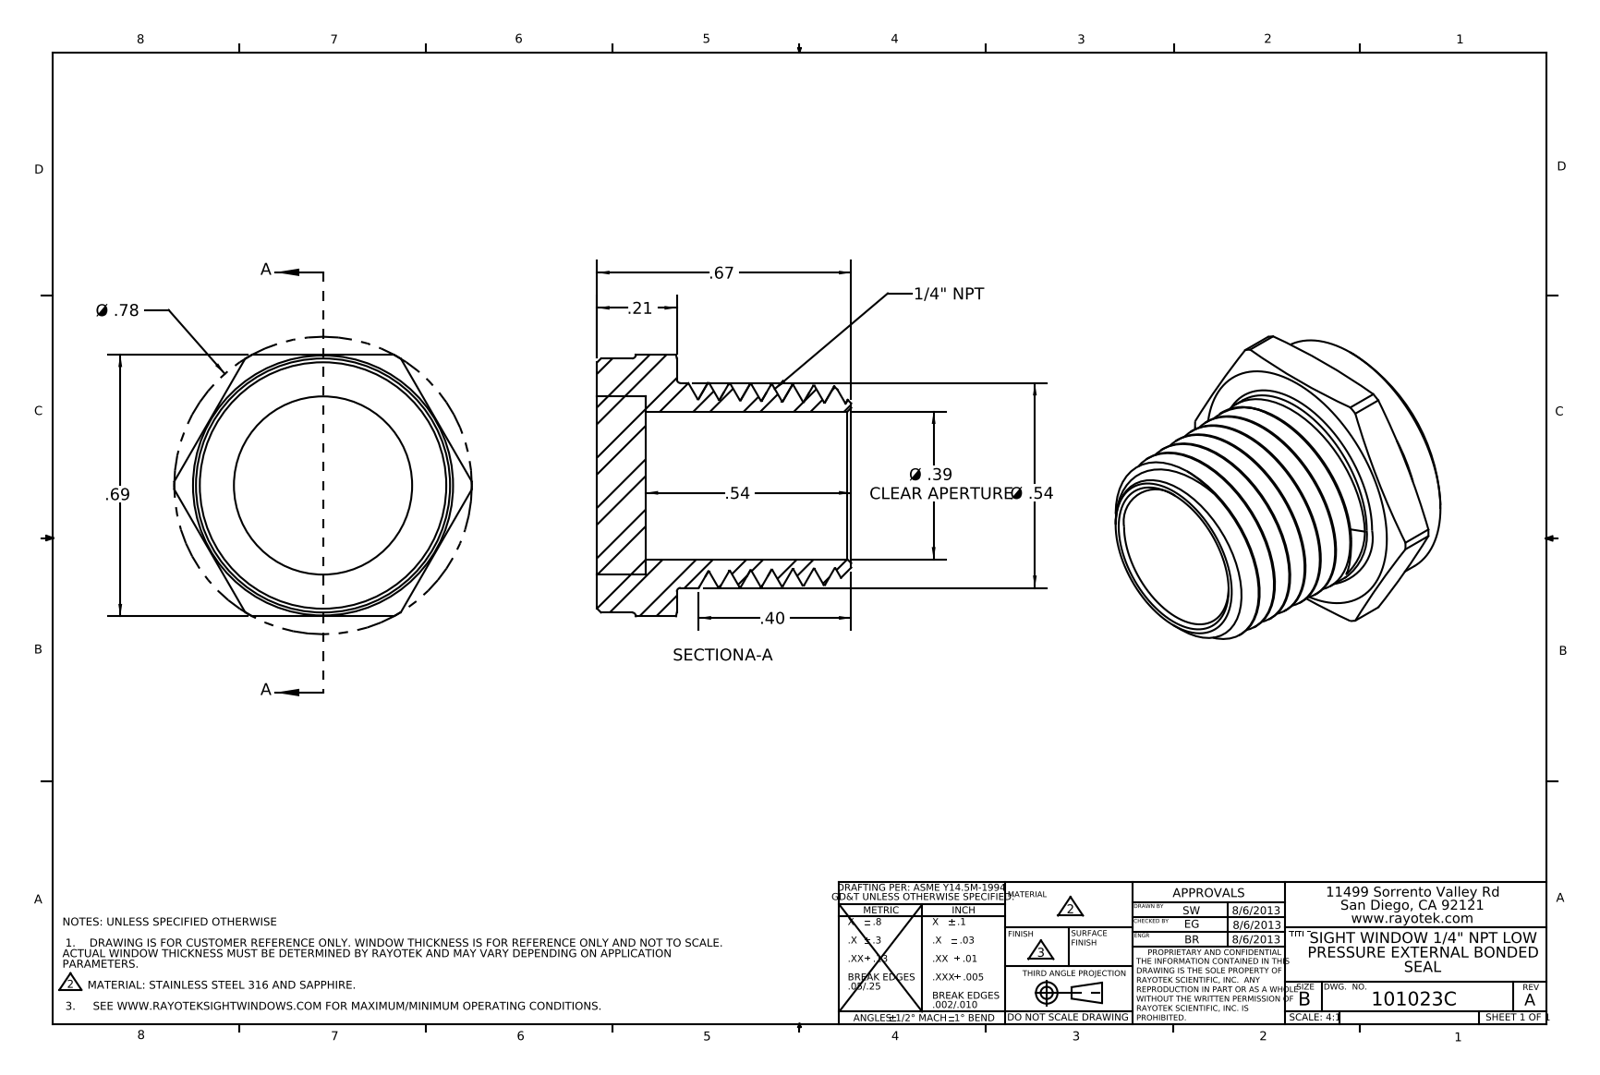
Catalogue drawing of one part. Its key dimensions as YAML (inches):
part_name: "403023"
step_written_by: "SolidWorks 2012 (AUTOMOTIVE_DESIGN)"
units: inches
bodies: {solids: 2, faces: 64, planar: 15, cylindrical: 18, other: 31}
overall_size: [0.785, 0.69, 0.67]
volume: 0.103
surface_area: 3.58
round_holes:
  - {diameter: 0.39, count: 1}
  - {diameter: 0.47, count: 1}
round_bosses_or_shafts:
  - {diameter: 0.67, count: 1}
  - {diameter: 0.54, count: 1}
partial_cylinders:
  - {radius: 0.392, count: 1}
face_to_face_distances: [0.128, 0.69, 0.21, 0.082, 0.67, 0.542, 0.46]
